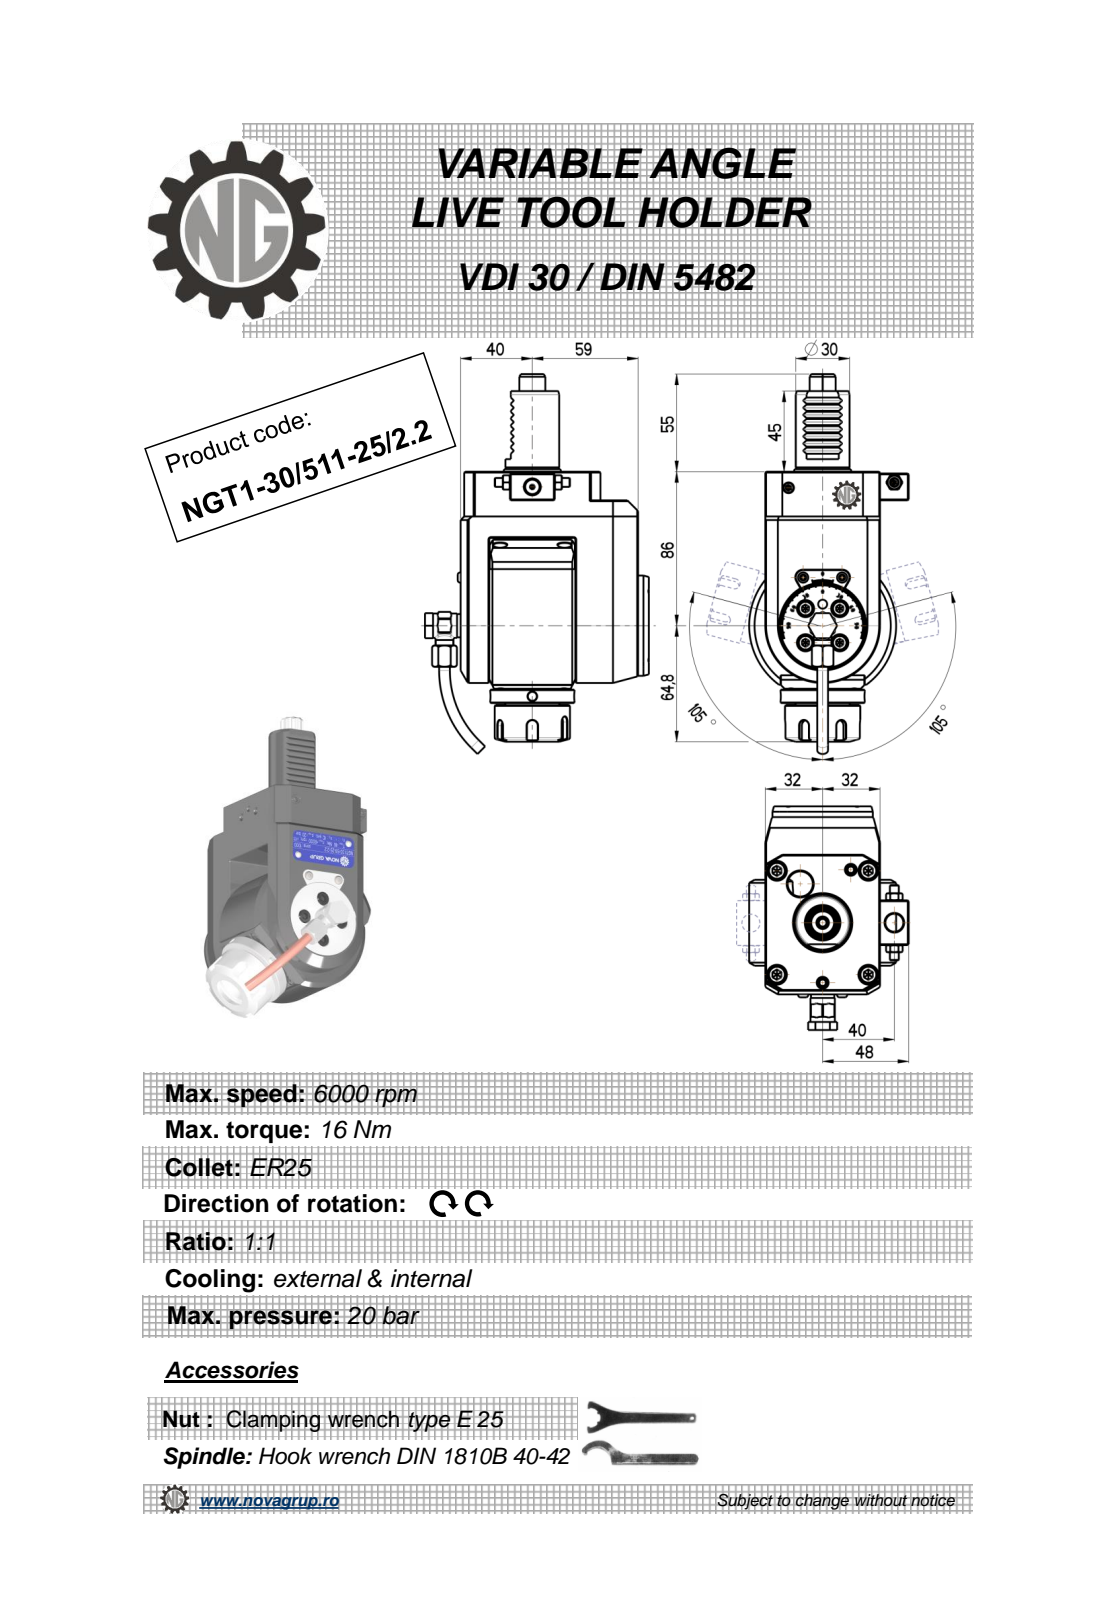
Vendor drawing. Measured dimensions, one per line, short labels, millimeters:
name: NGT1_30_511_25_2_2
written by: PRO/ENGINEER BY PARAMETRIC TECHNOLOGY CORPORATION, 2010280 (CONFIG_CONTROL_DESIGN)
unit: mm
bodies: 1 solid, 591 faces (226 planar, 166 cylindrical, 199 other)
size: 212.67 × 124.9 × 89
volume: 795 630 mm³; area: 74 498 mm²
holes: 3× ⌀4, 2× ⌀4.2, 2× ⌀5, 2× ⌀10, 1× ⌀3, 1× ⌀5.3, 1× ⌀6.2, 1× ⌀9, 1× ⌀9.5, 1× ⌀11, 1× ⌀20.3
bosses: 2× ⌀6, 2× ⌀5.7, 1× ⌀56, 1× ⌀47, 1× ⌀42, 1× ⌀35, 1× ⌀30, 1× ⌀13.6
rounds: 16× R2.91, 12× R0.26, 8× R0.3, 6× R0.16, 5× R3, 4× R0.5, 2× R1, 1× R5.75
face distances: 64, 16, 37, 6, 99, 105, 14, 21, 62, 35
hole spacings: 0.4, 39.45, 40, 49, 49.4, 63.25, 63.56, 89.44
